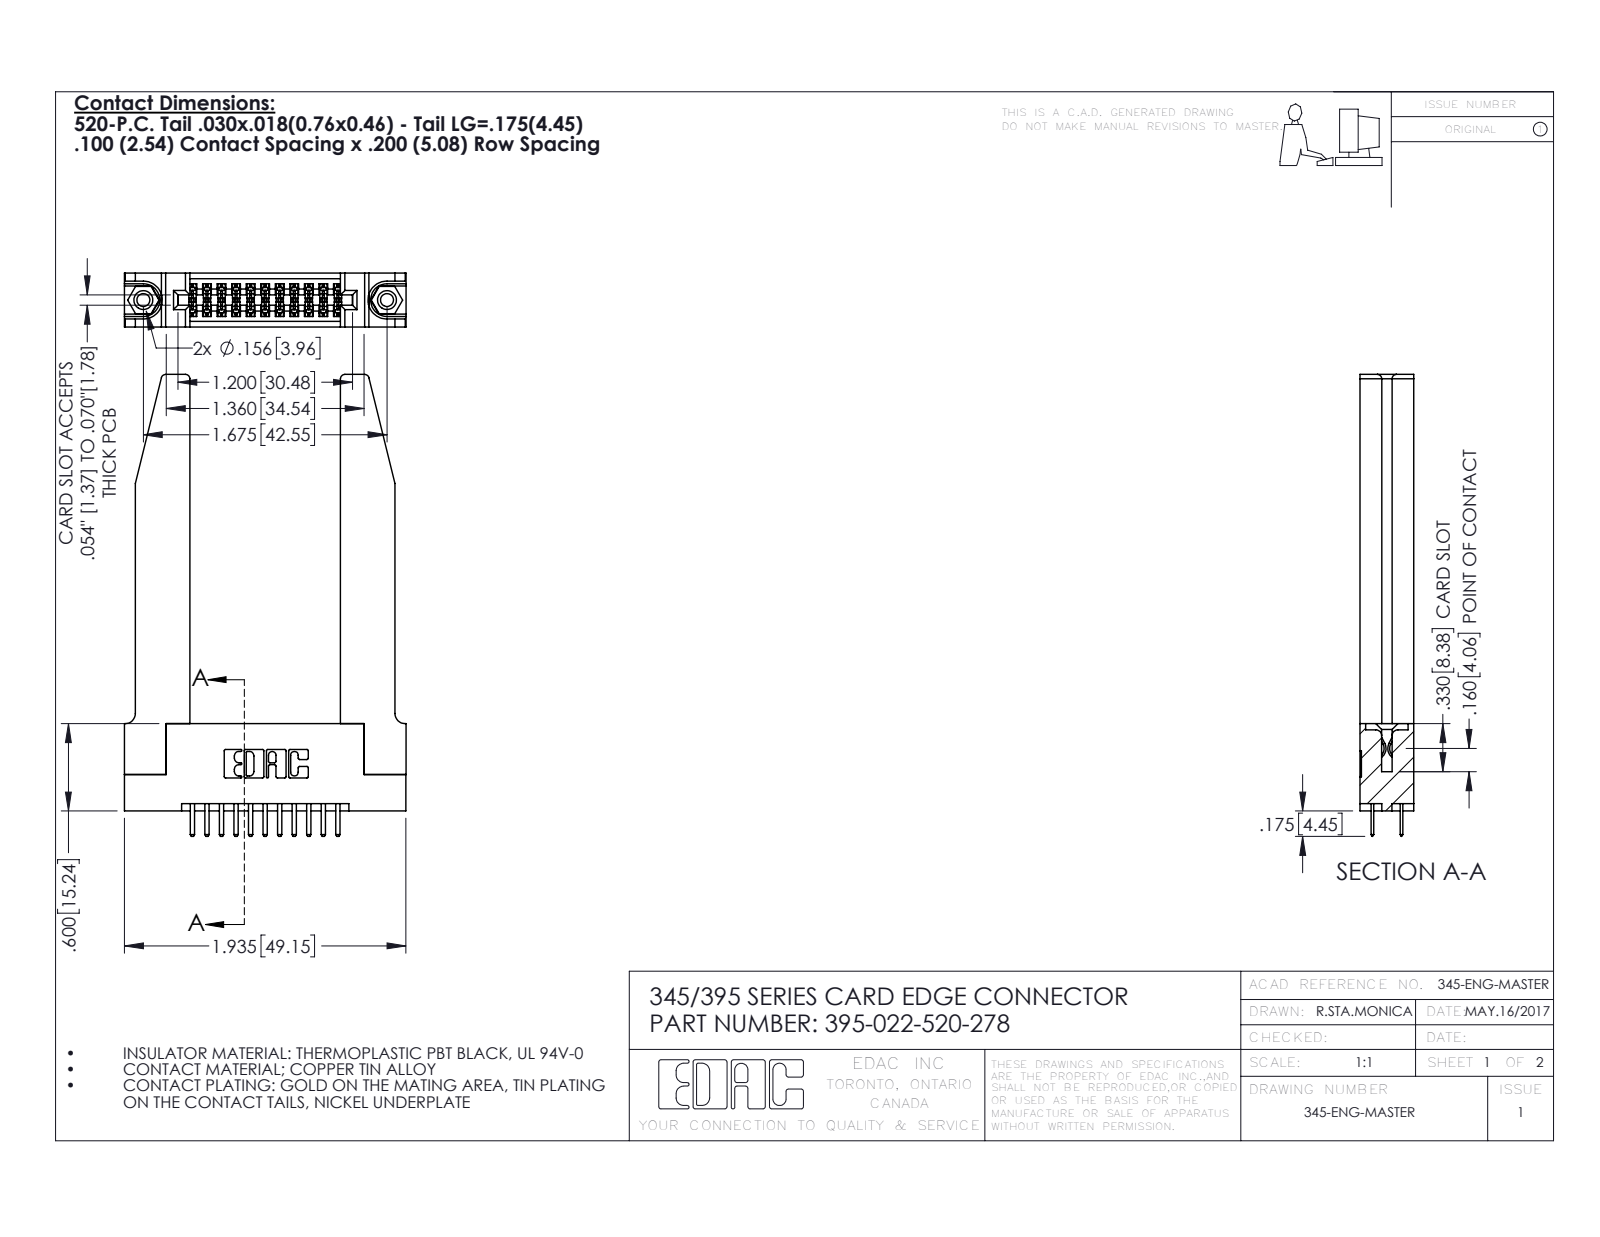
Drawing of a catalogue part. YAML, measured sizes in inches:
part_name: "345 Part_Flush Mounting Lugs - 0.156 Dia-TH; 345-220-078_345-220-078; 345-292-001_345-293-120; 395-022-520-278 (+1 more)"
step_written_by: "SolidWorks 2016 (CONFIG_CONTROL_DESIGN)"
units: inches
bodies: {solids: 27, faces: 1548, planar: 992, cylindrical: 504, other: 52}
overall_size: [3.175, 1.936, 0.37]
volume: 0.748
surface_area: 19.9
round_holes:
  - {diameter: 0.089, count: 2}
  - {diameter: 0.125, count: 2}
  - {diameter: 0.156, count: 2}
  - {diameter: 0.064, count: 1}
round_bosses_or_shafts:
  - {diameter: 0.155, count: 2}
partial_cylinders:
  - {radius: 0.006, count: 33}
  - {radius: 0.01, count: 26}
  - {radius: 0.01, count: 22}
  - {radius: 0.03, count: 8}
  - {radius: 0.007, count: 6}
  - {radius: 0.031, count: 6}
  - {radius: 0.026, count: 3}
  - {radius: 0.014, count: 2}
face_to_face_distances: [0.37, 0.072, 0.298, 0.2, 0.077, 0.15, 0.22, 0.148, 1.035, 0.225]
hole_center_spacings: [0.27, 1.443, 1.675]
